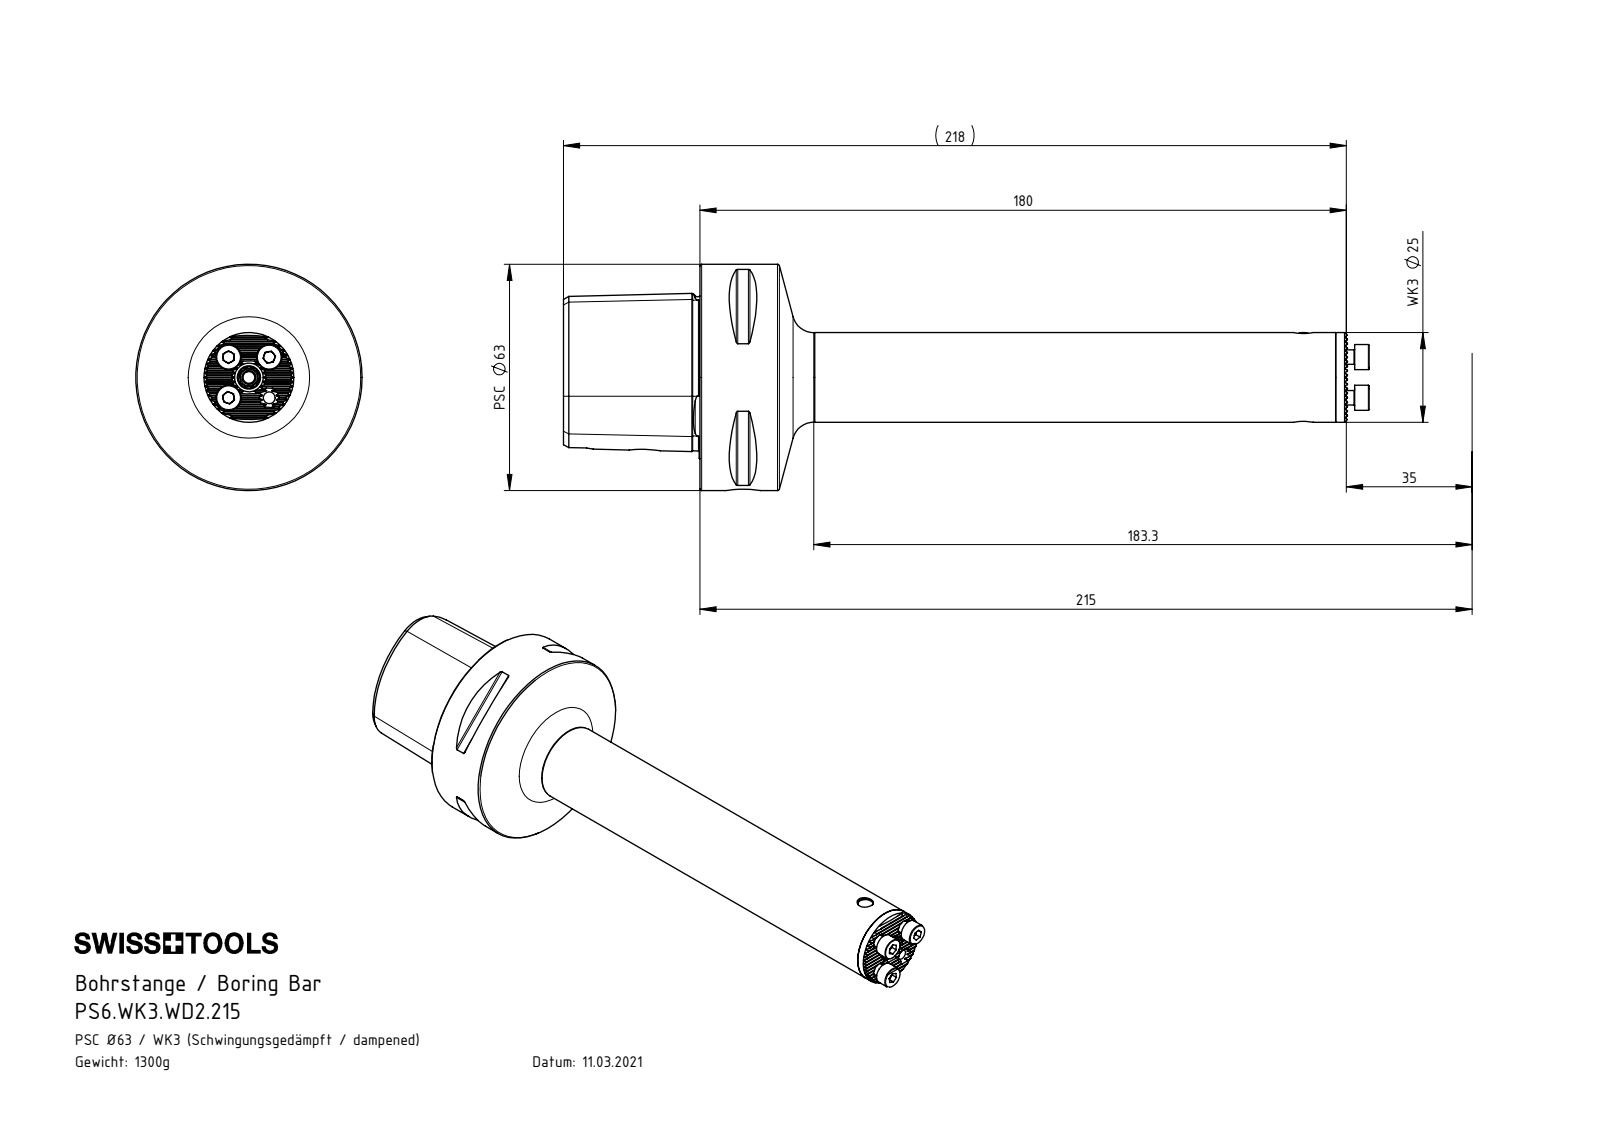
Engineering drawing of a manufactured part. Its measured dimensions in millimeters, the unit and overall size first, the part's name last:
Units: millimetres
Overall size (bounding box): 224.3 × 63 × 63
Round holes (diameter × count): ⌀3.3 ×5, ⌀5 ×1, ⌀5.5 ×1, ⌀6 ×1, ⌀6.5 ×1, ⌀6.8 ×1, ⌀7.4 ×1, ⌀8.1 ×1, ⌀9 ×1, ⌀10 ×1, ⌀10.2 ×1, ⌀11 ×1
Round bosses / shafts (diameter × count): ⌀7 ×3, ⌀4 ×3, ⌀63 ×1, ⌀25 ×1, ⌀21 ×1, ⌀20.7 ×1, ⌀20 ×1, ⌀17.8 ×1
Partial cylindrical surfaces — rounded edges, fillets, slot ends (radius × count): R0.12 ×19, R0.5 ×8, R6 ×1
Main face-to-face distances: 6, 38, 78.4, 3.2, 24.88, 4.33, 199, 161, 1.08, 9.2
Hole centre spacings: 8, 11.32, 16.01, 27.5, 156, 183.5
Volume: 168 480 mm³ · Surface area: 60 110 mm²
Bodies: 16 solids, 685 faces (237 planar, 169 cylindrical, 279 other)
Part name (STEP PRODUCT): WD2-ER1.021.019_A; DIN 6325_ø5x10-m6_2x6; WD2-ER1.008.067_A; PS6-WD2.085.177_A_mit Stiftbohrung (+8 more)
STEP written by: SolidWorks 2017 (AUTOMOTIVE_DESIGN)
